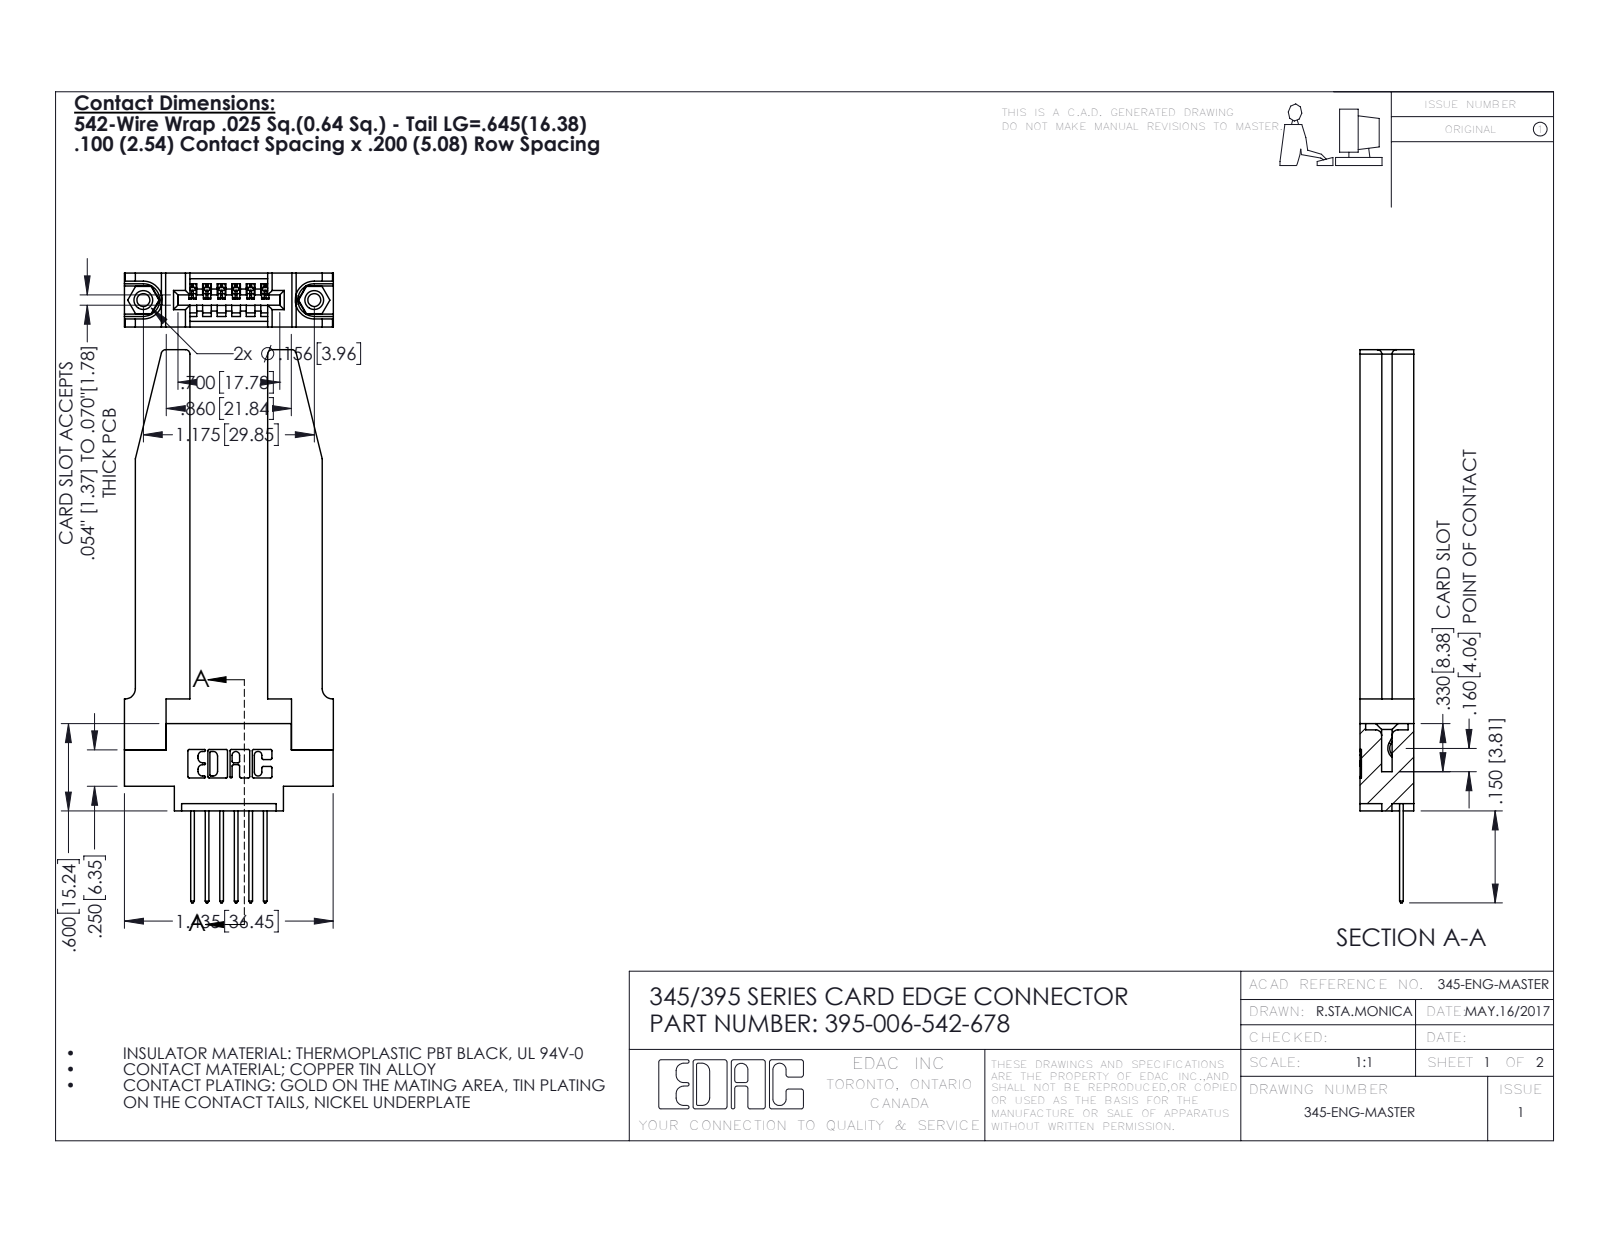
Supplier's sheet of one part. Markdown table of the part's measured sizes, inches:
| quantity | value |
| --- | --- |
| part name | 345-220-078_345-220-078; 395-006-542-678; 345 Part_0.170 Offset - 0.156 Dia-TH; 345-250-001_345-250-001-102 (+1 more) |
| STEP written by | SolidWorks 2016 (CONFIG_CONTROL_DESIGN) |
| units | inches |
| bodies | 11 solids, 712 faces (466 planar, 194 cylindrical, 52 other) |
| overall size | 3.802 × 1.436 × 0.37 |
| volume | 0.661 in³ |
| surface area | 16.5 in² |
| round holes (diameter × count) | 0.089 × 2, 0.125 × 2, 0.156 × 2, 0.064 × 1 |
| round bosses / shafts (diameter × count) | 0.155 × 2 |
| partial cylindrical surfaces (radius × count) | 0.01 × 22, 0.006 × 12, 0.01 × 12, 0.03 × 8, 0.007 × 6, 0.031 × 6, 0.026 × 3, 0.031 × 2 |
| main face-to-face distances | 0.37, 0.15, 0.22, 0.072, 0.535, 0.148, 0.298, 0.077, 0.095, 0.071 |
| hole center spacings | 0.27, 0.946, 1.175 |
